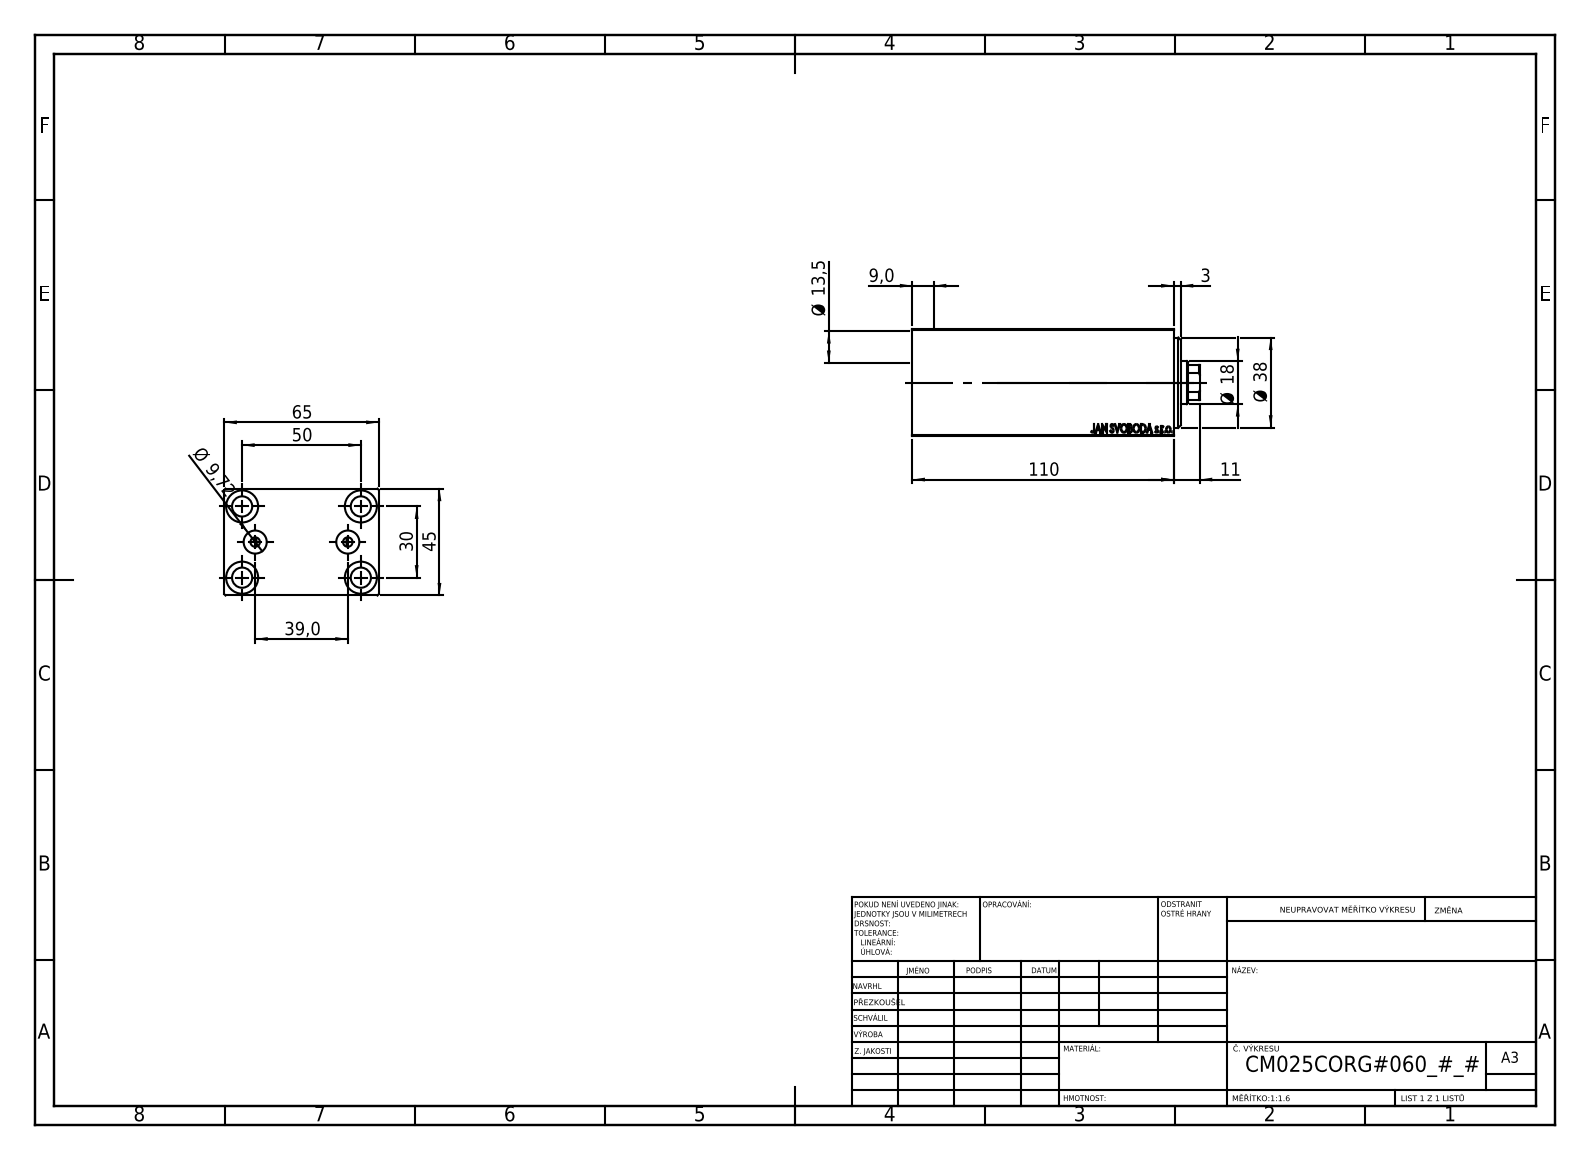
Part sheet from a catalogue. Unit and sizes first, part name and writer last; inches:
Units: inches
Overall size (bounding box): 4.764 × 2.559 × 1.772
Round holes (diameter × count): ⌀0.335 ×5, ⌀0.531 ×4, ⌀0.157 ×2, ⌀0.383 ×2, ⌀0.709 ×1, ⌀0.846 ×1, ⌀0.984 ×1, ⌀1.063 ×1, ⌀1.496 ×1
Partial cylindrical surfaces — rounded edges, fillets, slot ends (radius × count): R0.335 ×1
Main face-to-face distances: 1.772, 2.559, 0.236, 3.898, 4.094, 4.134, 0.197, 4.331, 0.118, 0.315
Hole centre spacings: 0.629, 1.148, 1.849, 0.768, 1.181, 1.969, 2.296, 1.535
Volume: 16.87 in³ · Surface area: 102.8 in²
Bodies: 3 solids, 858 faces (408 planar, 56 cylindrical, 394 other)
Part name (STEP PRODUCT): V450CM_VC_B; V450CM_C_VCP; V450CM_C_Body
STEP written by: SolidWorks 2019 (CONFIG_CONTROL_DESIGN)
